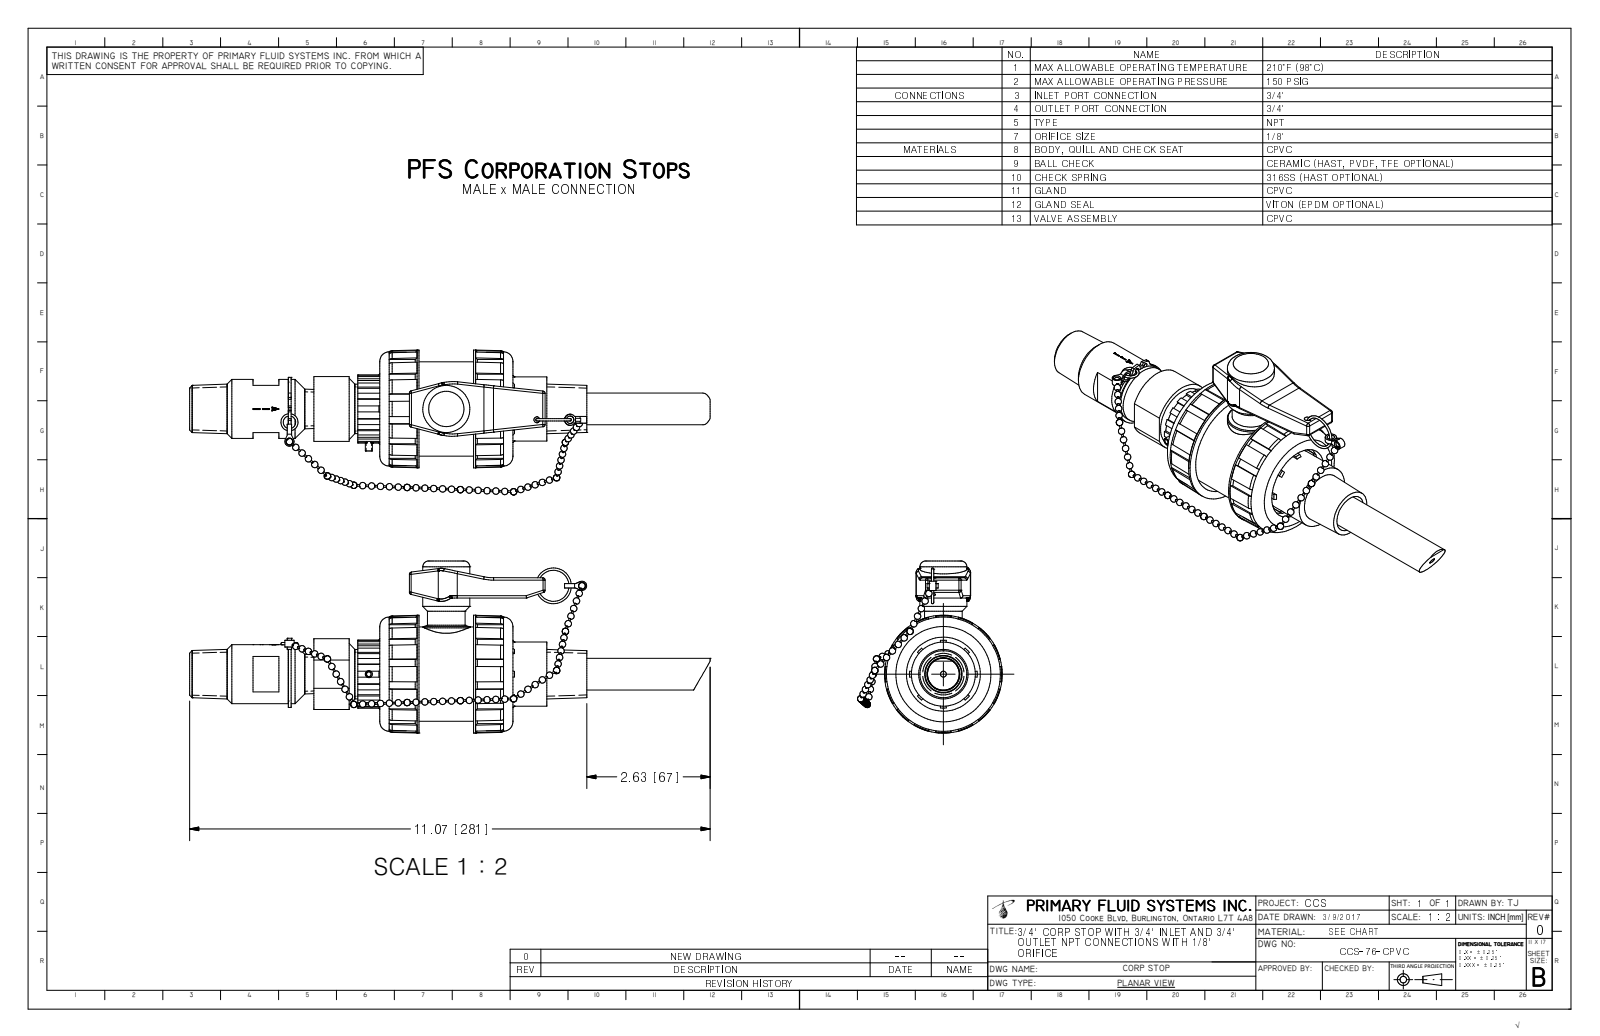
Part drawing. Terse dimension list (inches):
name: CCS-76-CPVC_R0
written by: Autodesk Inventor 2009 (AUTOMOTIVE_DESIGN)
unit: in
bodies: 1 solid, 606 faces (225 planar, 145 cylindrical, 236 other)
size: 11.069 × 3.65 × 3.075
volume: 19.34 in³; area: 107 in²
holes: 1× ⌀0.098, 1× ⌀0.125, 1× ⌀0.25, 1× ⌀0.469, 1× ⌀0.56, 1× ⌀1.57, 1× ⌀2.16
bosses: 1× ⌀2.5, 1× ⌀2, 1× ⌀1.801, 1× ⌀1.36, 1× ⌀1.343, 1× ⌀1.25, 1× ⌀1.14, 1× ⌀1
rounds: 21× R0.05, 3× R1, 2× R0.054, 2× R0.197, 1× R0.351, 1× R0.624, 1× R0.72, 1× R0.75
face distances: 0.205, 2.625, 0.835, 1.995, 0.63, 1.79, 0.465, 2.83, 2.42, 1.16
hole spacings: 0.657
